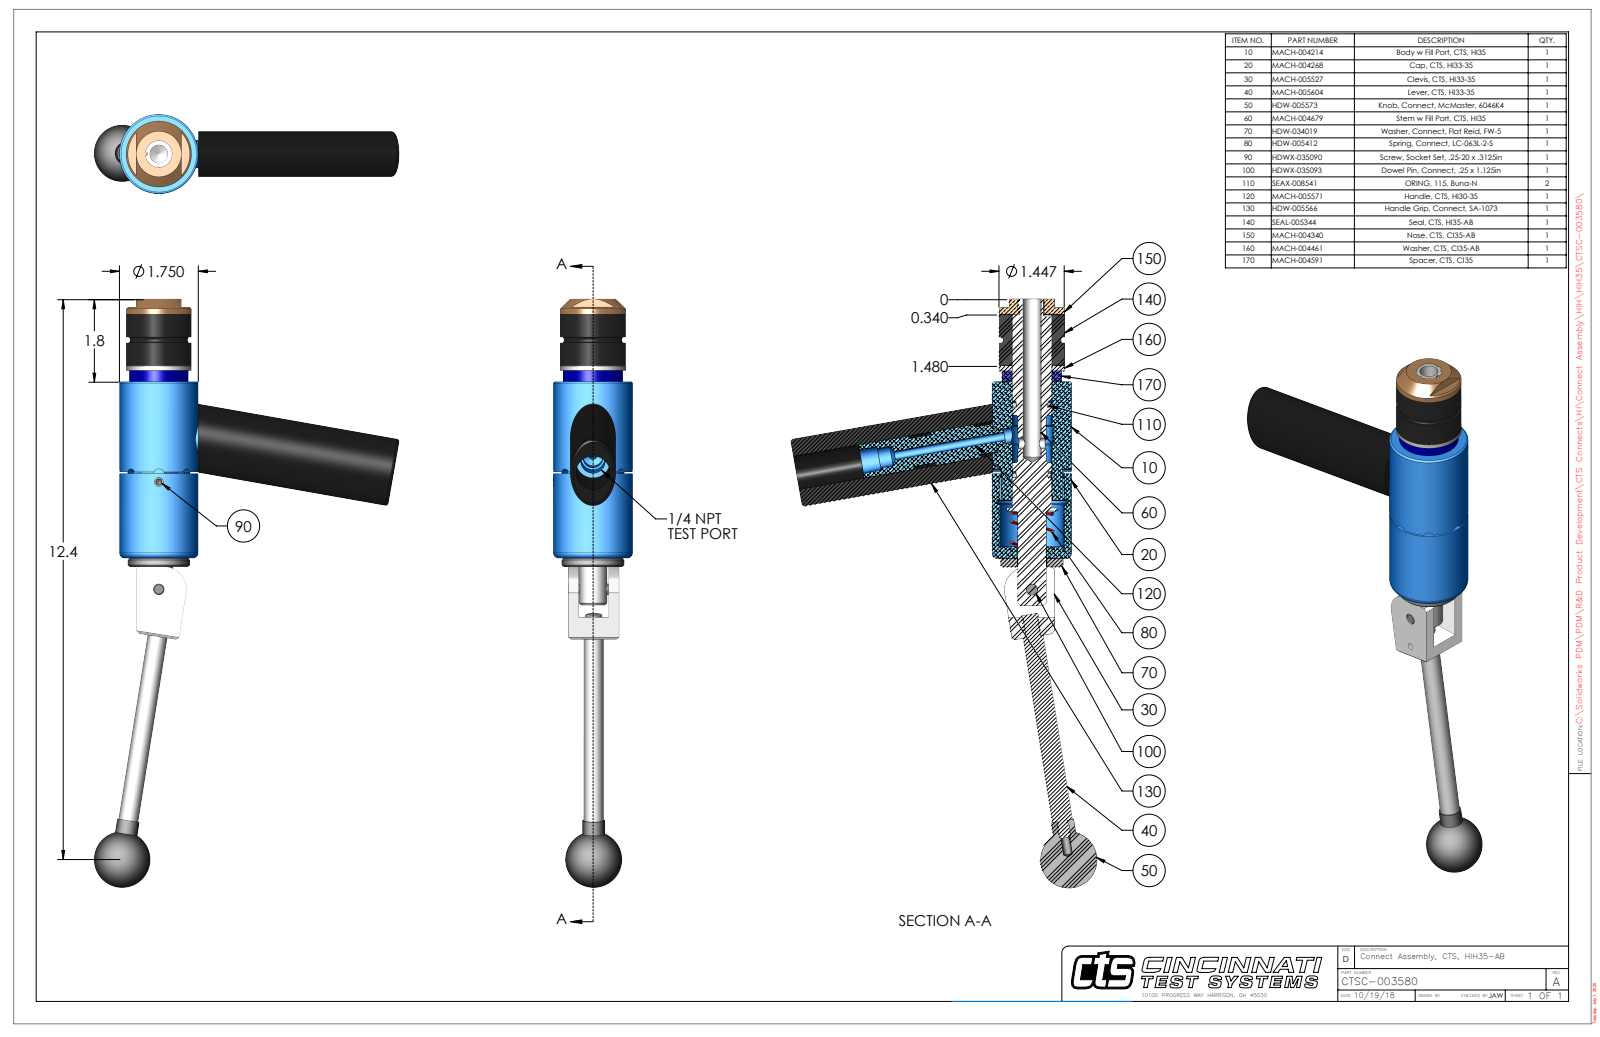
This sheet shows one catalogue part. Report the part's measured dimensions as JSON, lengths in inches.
{"part_name": "CTSC-003580", "step_written_by": "SolidWorks 2023 (AUTOMOTIVE_DESIGN)", "units": "inches", "bodies": {"solids": 12, "faces": 307, "planar": 110, "cylindrical": 126, "other": 71}, "overall_size": [13.042, 6.763, 1.75], "volume_in3": 19.21, "surface_area_in2": 127, "round_holes": [[0.201, 2], [0.15, 1], [0.187, 1], [0.249, 1], [0.25, 1], [0.251, 1], [0.313, 1], [0.406, 1], [0.438, 1], [0.531, 1], [0.635, 1], [0.656, 1]], "round_bosses_or_shafts": [[0.25, 2], [1.75, 1], [1.447, 1], [1.38, 1], [1.312, 1], [0.869, 1], [0.75, 1], [0.625, 1]], "partial_cylinders_radius": [[0.125, 4], [0.029, 2], [0.166, 1], [0.248, 1], [0.33, 1], [0.5, 1], [0.695, 1], [0.818, 1]], "face_to_face_distances": [5.405, 1.49, 3.915, 1.14, 0.35, 4.265, 1.25, 0.11, 0.24, 4.155], "hole_center_spacings": [0.74, 2.376, 3.116]}
